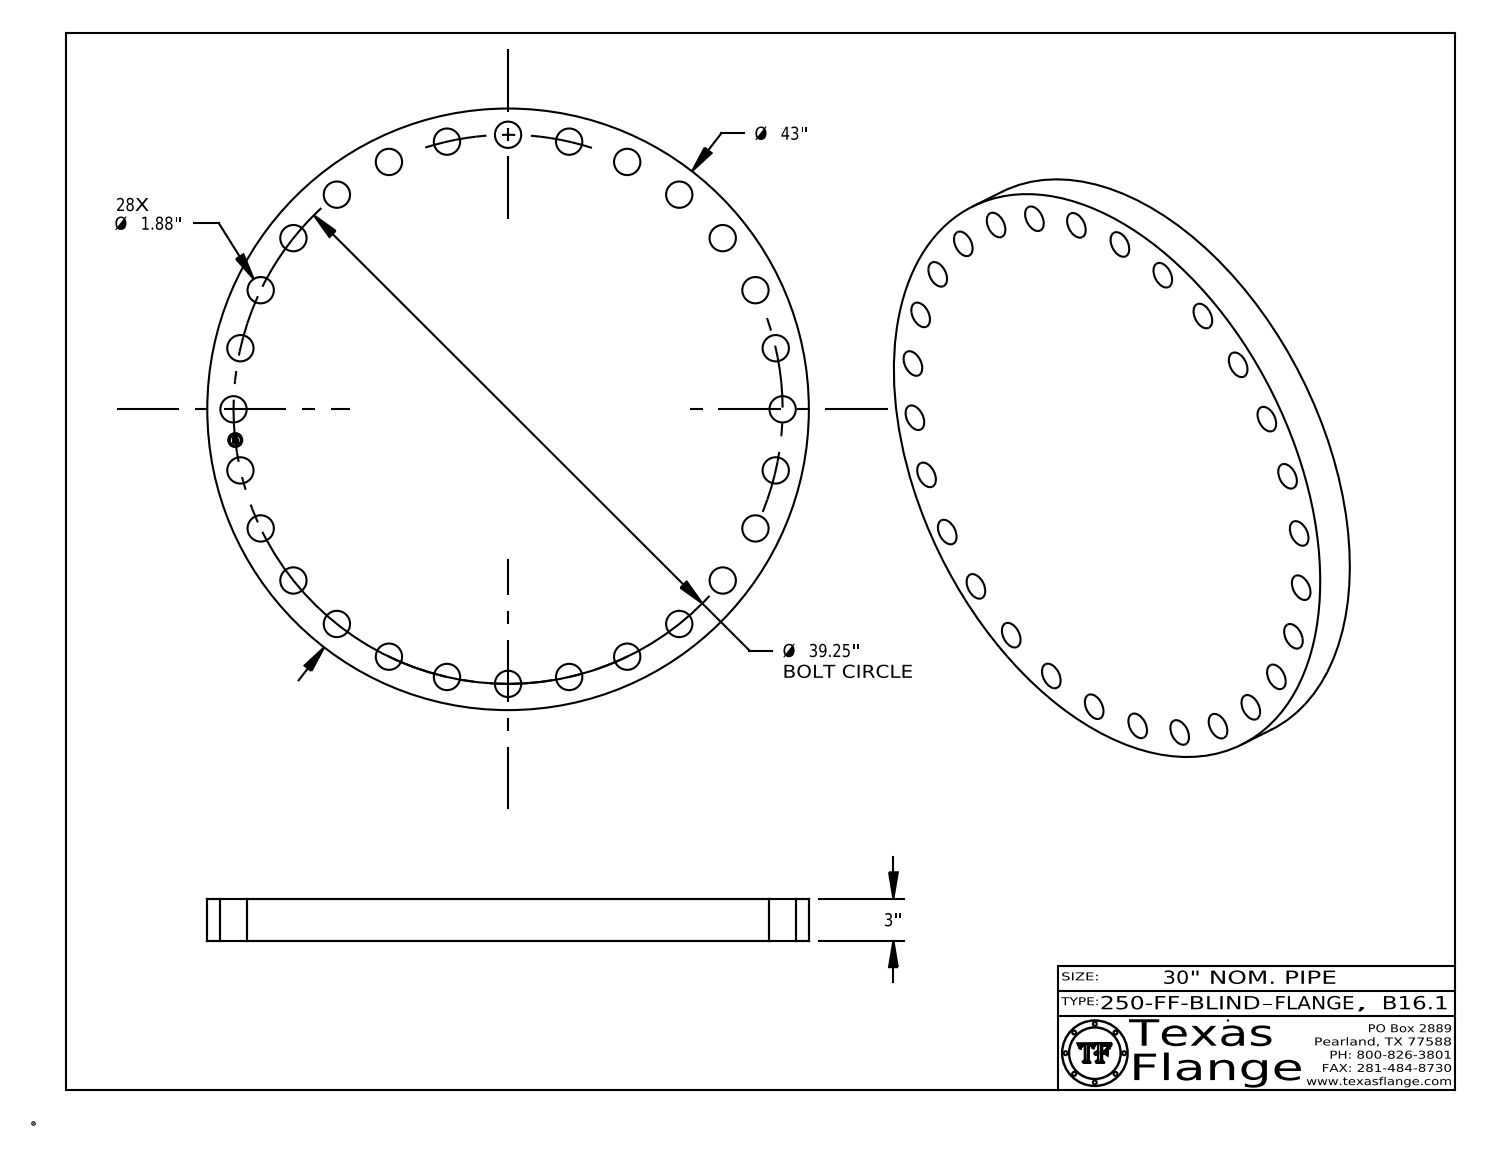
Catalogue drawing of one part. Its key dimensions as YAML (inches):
part_name: "250-FF-BLIND, Series B16.1"
step_written_by: "CATIA V5 STEP AP214 (AUTOMOTIVE_DESIGN)"
units: inches
bodies: {solids: 1, faces: 445, planar: 367, cylindrical: 78, other: 0}
overall_size: [43, 43, 3]
volume: 4123
surface_area: 3651
round_holes:
  - {diameter: 1.88, count: 28}
  - {diameter: 1, count: 1}
round_bosses_or_shafts:
  - {diameter: 0.061, count: 8}
  - {diameter: 43, count: 1}
  - {diameter: 0.788, count: 1}
face_to_face_distances: [3, 2.985, 0.015, 0.298, 0.293, 0.054, 0.193, 0.248, 0.044, 0.15]
hole_center_spacings: [4.394, 8.734, 12.963, 17.03, 20.882, 35.363, 24.472, 33.234]
